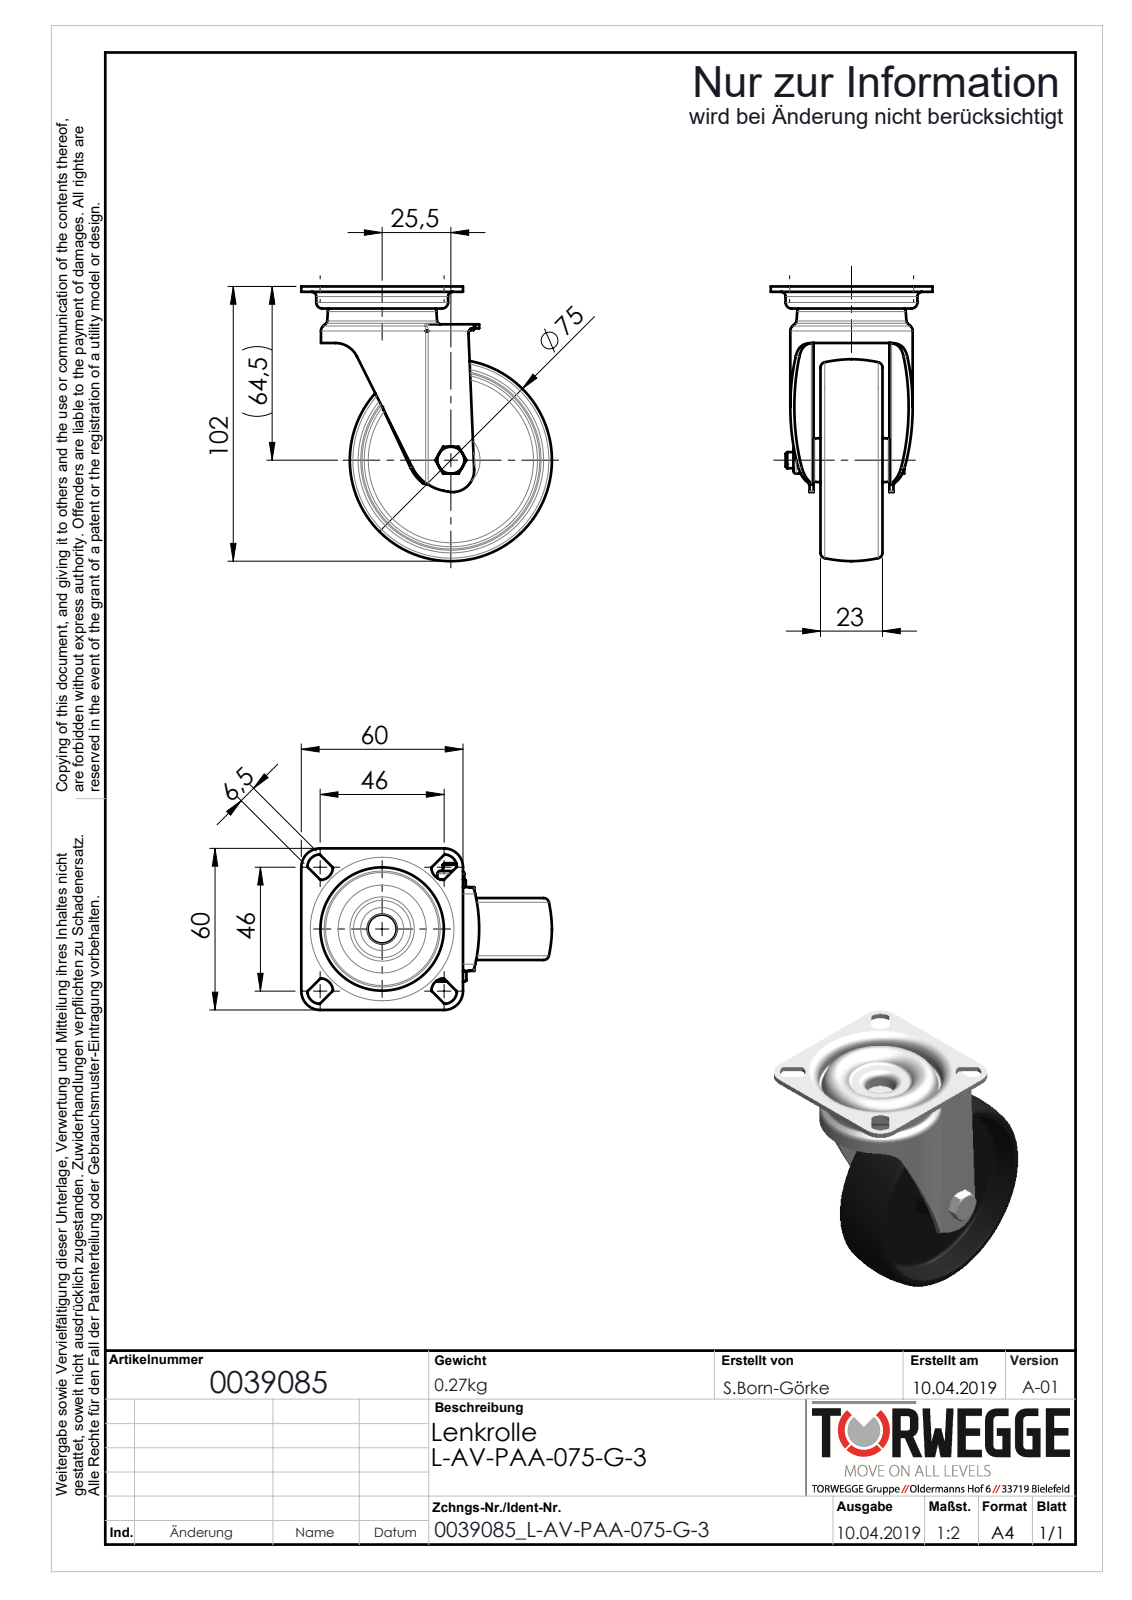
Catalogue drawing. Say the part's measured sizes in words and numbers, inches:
The part is named "0039085_L-AV-PAA-075-G-3_(A-01)". Its 3-D file was written by "SolidWorks 2018 (AUTOMOTIVE_DESIGN)". It is 7 solids with 313 faces: 75 planar, 91 cylindrical and 147 other. Overall it measures 4.016 by 3.661 by 2.362 inches. Its volume is 4.225 cubic inches and its surface area 70.86 square inches. Round holes: 1 of diameter 0.197, 1 of diameter 0.236, 1 of diameter 0.244, 1 of diameter 0.281, 1 of diameter 0.315, 1 of diameter 1.004, 1 of diameter 1.803. Round bosses or shafts: 1 of diameter 1.925, 1 of diameter 1.427, 1 of diameter 1.13, 1 of diameter 0.974, 1 of diameter 0.394. Partial cylindrical surfaces (rounded edges, fillets, slot ends): 16 of radius 0.024, 4 of radius 0.187, 4 of radius 0.276, 2 of radius 0.039, 2 of radius 0.051, 2 of radius 0.098, 2 of radius 0.11, 1 of radius 0.079. The main face-to-face distances are 0.157, 0.059, 0.533, 0.474, 0.691, 1.165, 0.632, 0.079, 0.549, 0.244.
